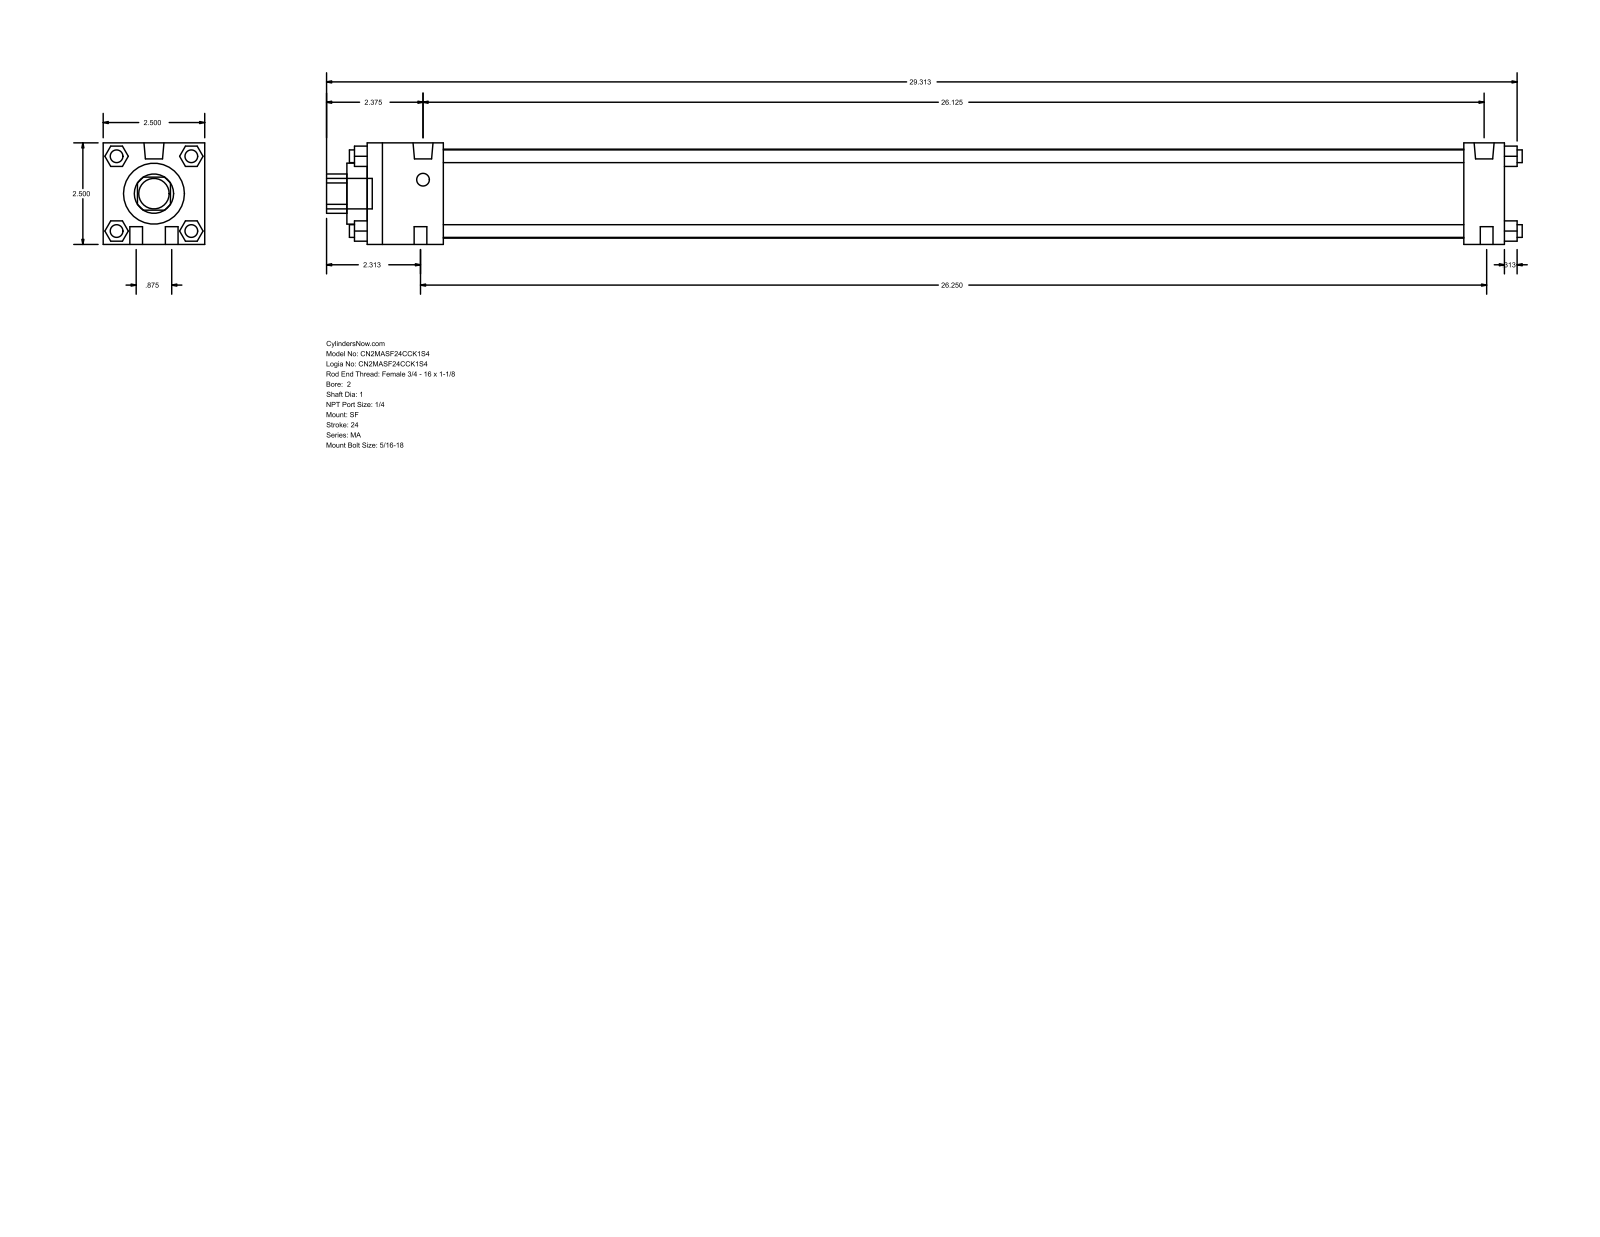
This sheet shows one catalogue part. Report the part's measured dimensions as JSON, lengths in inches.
{"part_name": "MA_SF__0200_1", "step_written_by": "GSSL Pune (CONFIG_CONTROL_DESIGN)", "units": "inches", "bodies": {"solids": 0, "faces": 124, "planar": 94, "cylindrical": 30, "other": 0}, "overall_size": [29.437, 2.5, 2.5], "round_holes": [[1, 1], [1.5, 1], [2.19, 1]], "round_bosses_or_shafts": [[0.313, 10], [0.492, 2], [0.75, 1]], "partial_cylinders_radius": [[0.484, 1]], "face_to_face_distances": [2.5, 28, 0.5, 1, 27, 1.875, 25.125, 26.125, 1.593, 0.92]}
